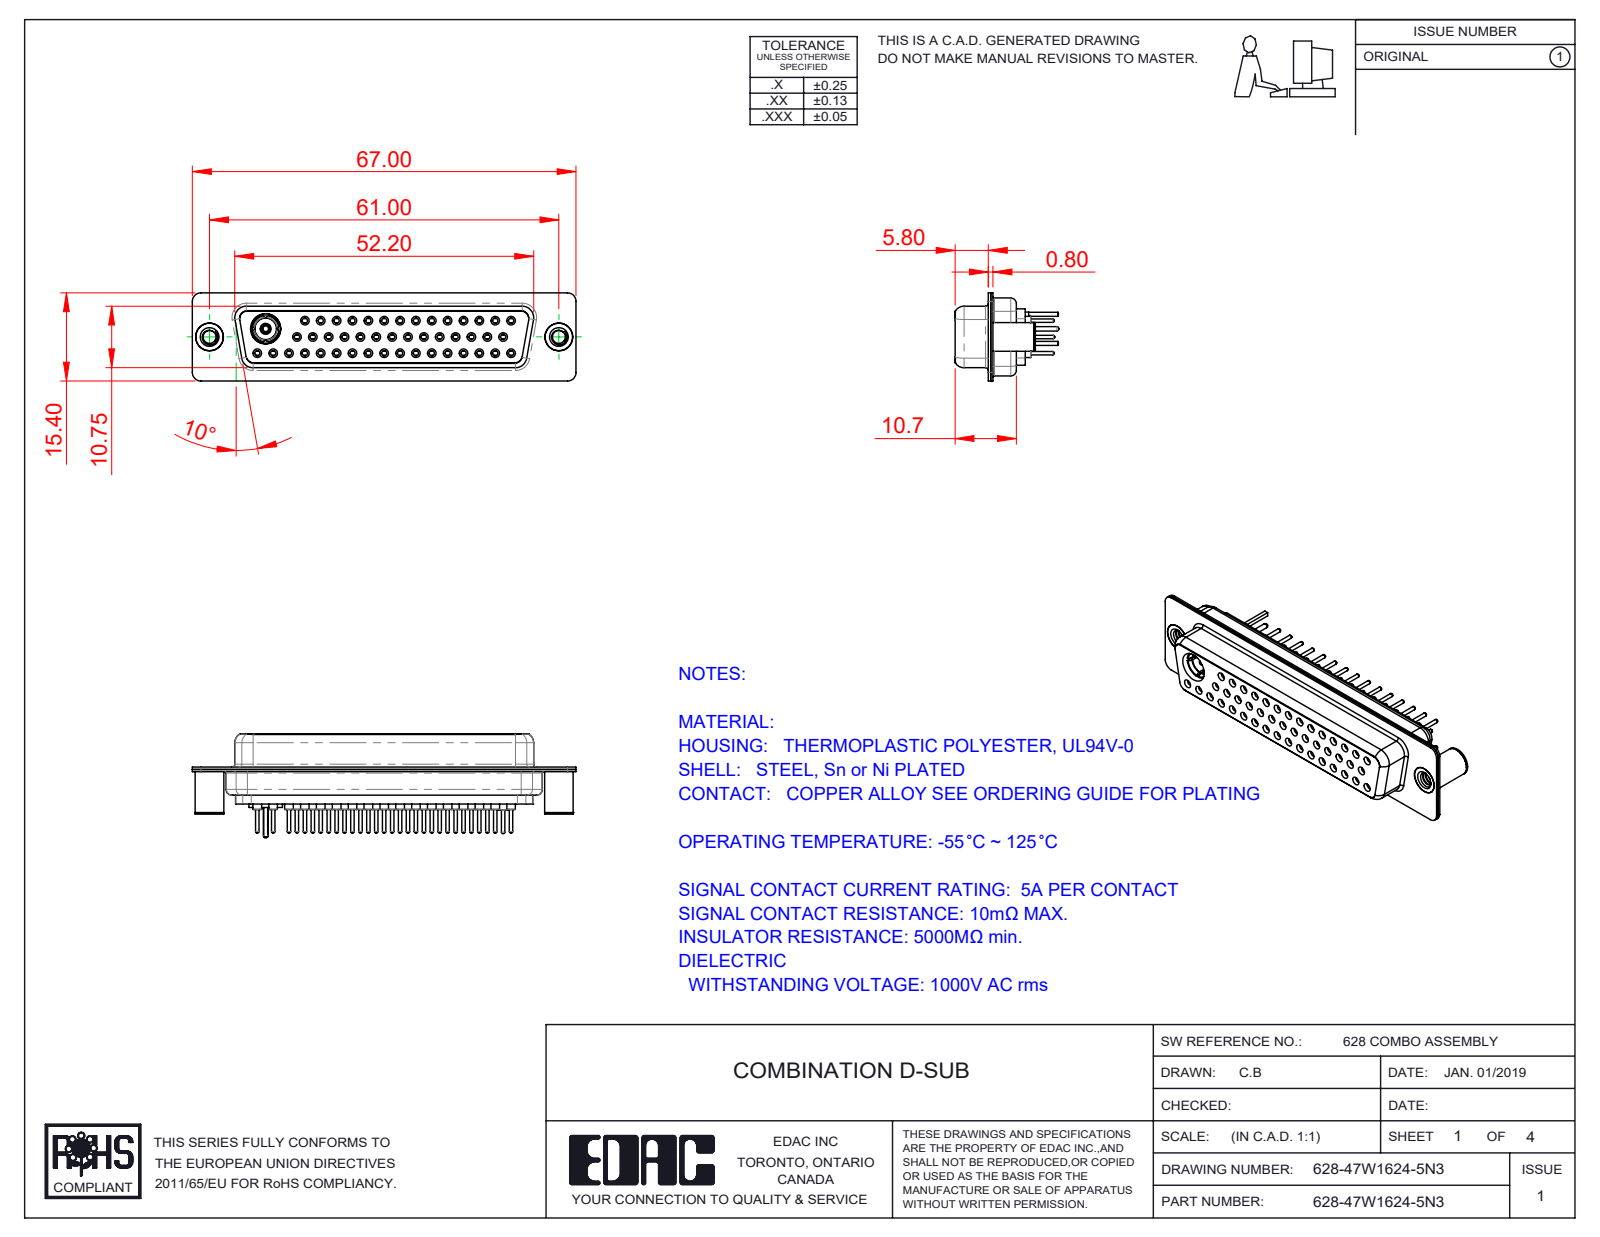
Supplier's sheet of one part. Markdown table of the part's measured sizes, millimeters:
| quantity | value |
| --- | --- |
| part name | 628Combo Threaded Board Spacer_3; 628Combo Contact Row 2_24; 628Combo Shell Rear_50 Contacts; Co-Ax Plug_Straight PC Tail (+8 more) |
| STEP written by | SolidWorks 2016 (CONFIG_CONTROL_DESIGN) |
| units | millimeters |
| bodies | 55 solids, 2957 faces (811 planar, 1072 cylindrical, 1074 other) |
| overall size | 67 × 18.15 × 15.4 |
| volume | 7 167 mm³ |
| surface area | 15 138 mm² |
| round holes (diameter × count) | 1.1 × 47, 1.5 × 46, 0.9 × 45, 2 × 45, 1.6 × 31, 1.7 × 14, 4.85 × 3, 2.26 × 2, 3.26 × 2, 4 × 2, 4.05 × 2, 2.83 × 1 |
| round bosses / shafts (diameter × count) | 2.2 × 46, 0.6 × 46, 1.6 × 15, 5 × 3, 4.95 × 2, 4.8 × 2, 5.85 × 1, 5.2 × 1 |
| partial cylindrical surfaces (radius × count) | 1.5 × 16, 1.35 × 12, 2 × 12, 1.6 × 8, 0.25 × 4, 0.5 × 4, 0.6 × 4, 0.65 × 4 |
| main face-to-face distances | 0.4, 6.05, 6.45, 11.33, 1.87, 12.25, 6.2, 5.8, 10.35, 10.93 |
| hole center spacings | 3.16, 2.77, 5.54, 8.31, 11.08, 13.85, 16.62, 19.39 |
